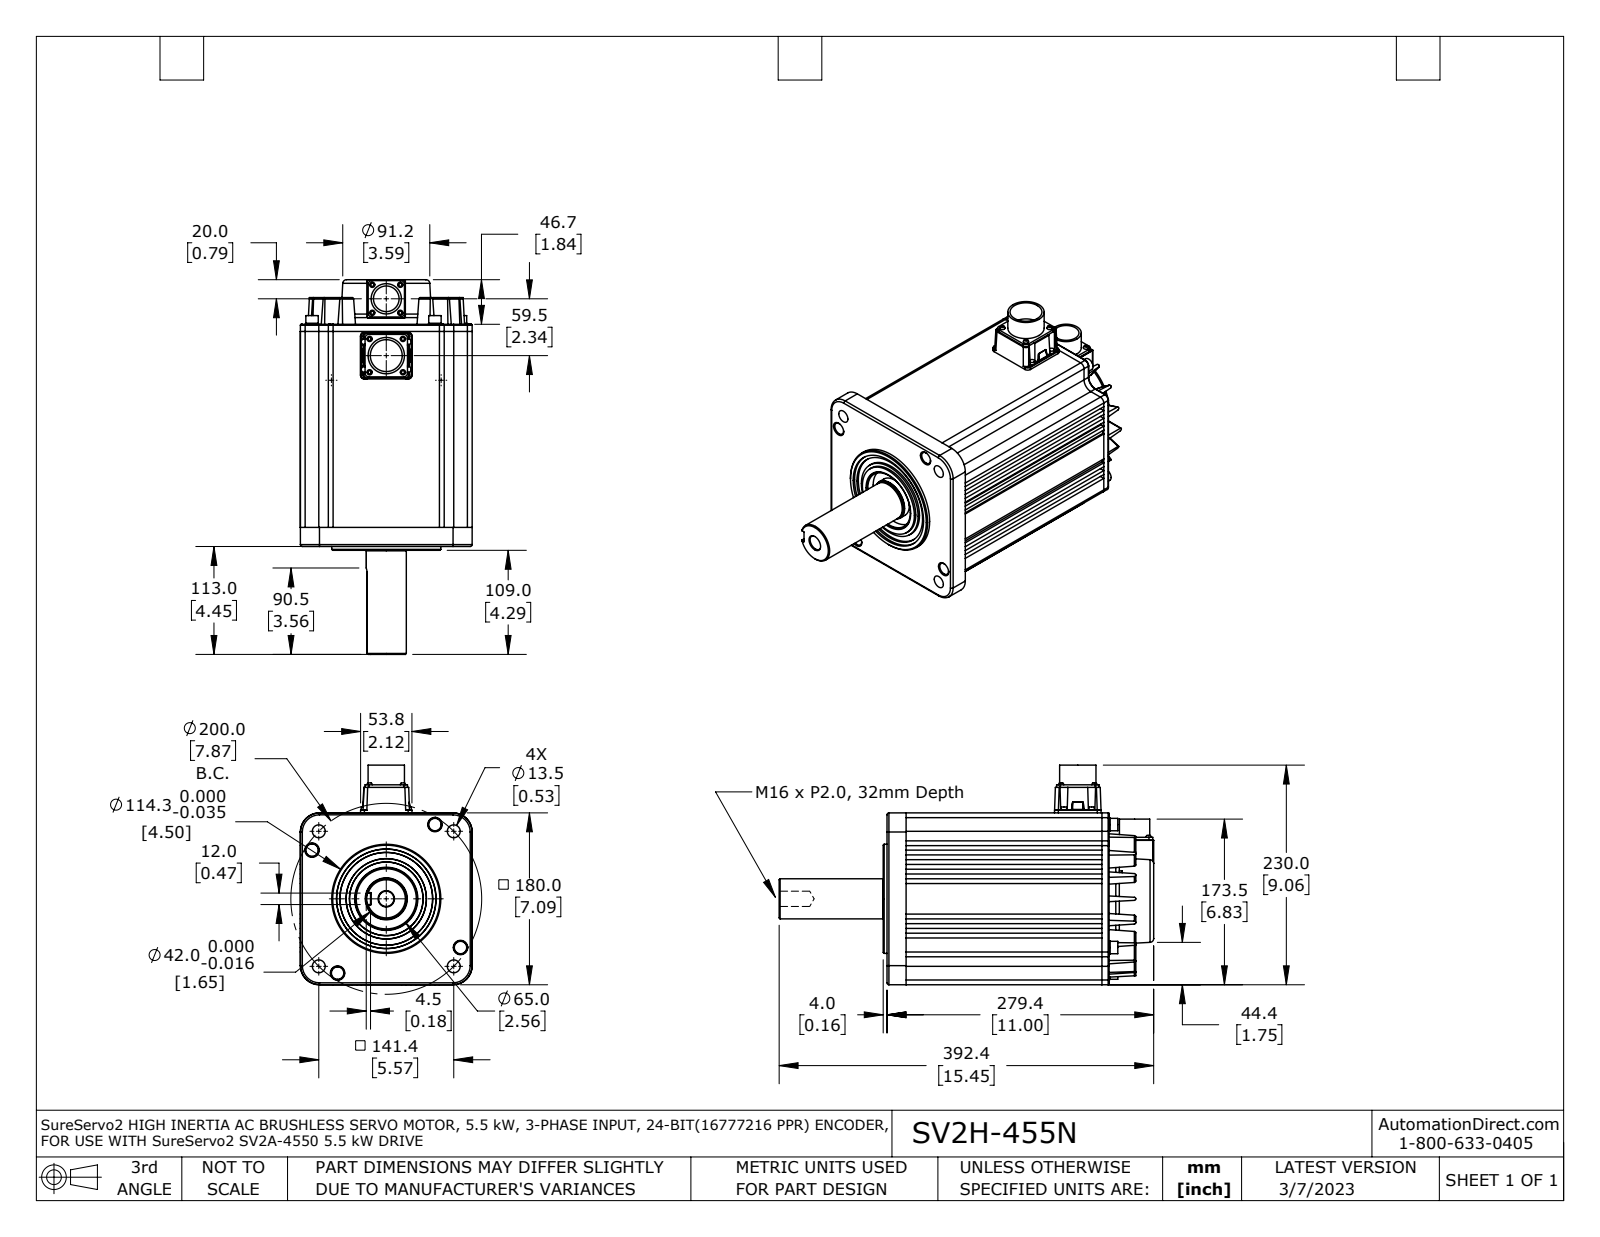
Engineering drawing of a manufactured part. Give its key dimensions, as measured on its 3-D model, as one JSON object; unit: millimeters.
{"part_name": "SV2H-455N", "step_written_by": "SolidWorks 2021 (AUTOMOTIVE_DESIGN)", "units": "millimeters", "bodies": {"solids": 1, "faces": 624, "planar": 309, "cylindrical": 211, "other": 104}, "overall_size": [392.4, 230, 180], "volume_mm3": 7323000, "surface_area_mm2": 365000, "round_holes": [[13.5, 4], [16, 1], [26.9, 1], [33.5, 1], [63, 1]], "round_bosses_or_shafts": [[5.5, 7], [13.4, 4], [13, 4], [8, 4], [116, 1], [114.3, 1], [44, 1], [42.5, 1]], "partial_cylinders_radius": [[0.5, 22], [1.6, 16], [4, 16], [5, 16], [1, 12], [2, 4], [10, 4], [20, 4]], "face_to_face_distances": [5, 10, 180, 29.3, 15, 150.7, 77, 82, 72, 20], "hole_center_spacings": [100, 141.4, 200, 59.5]}
